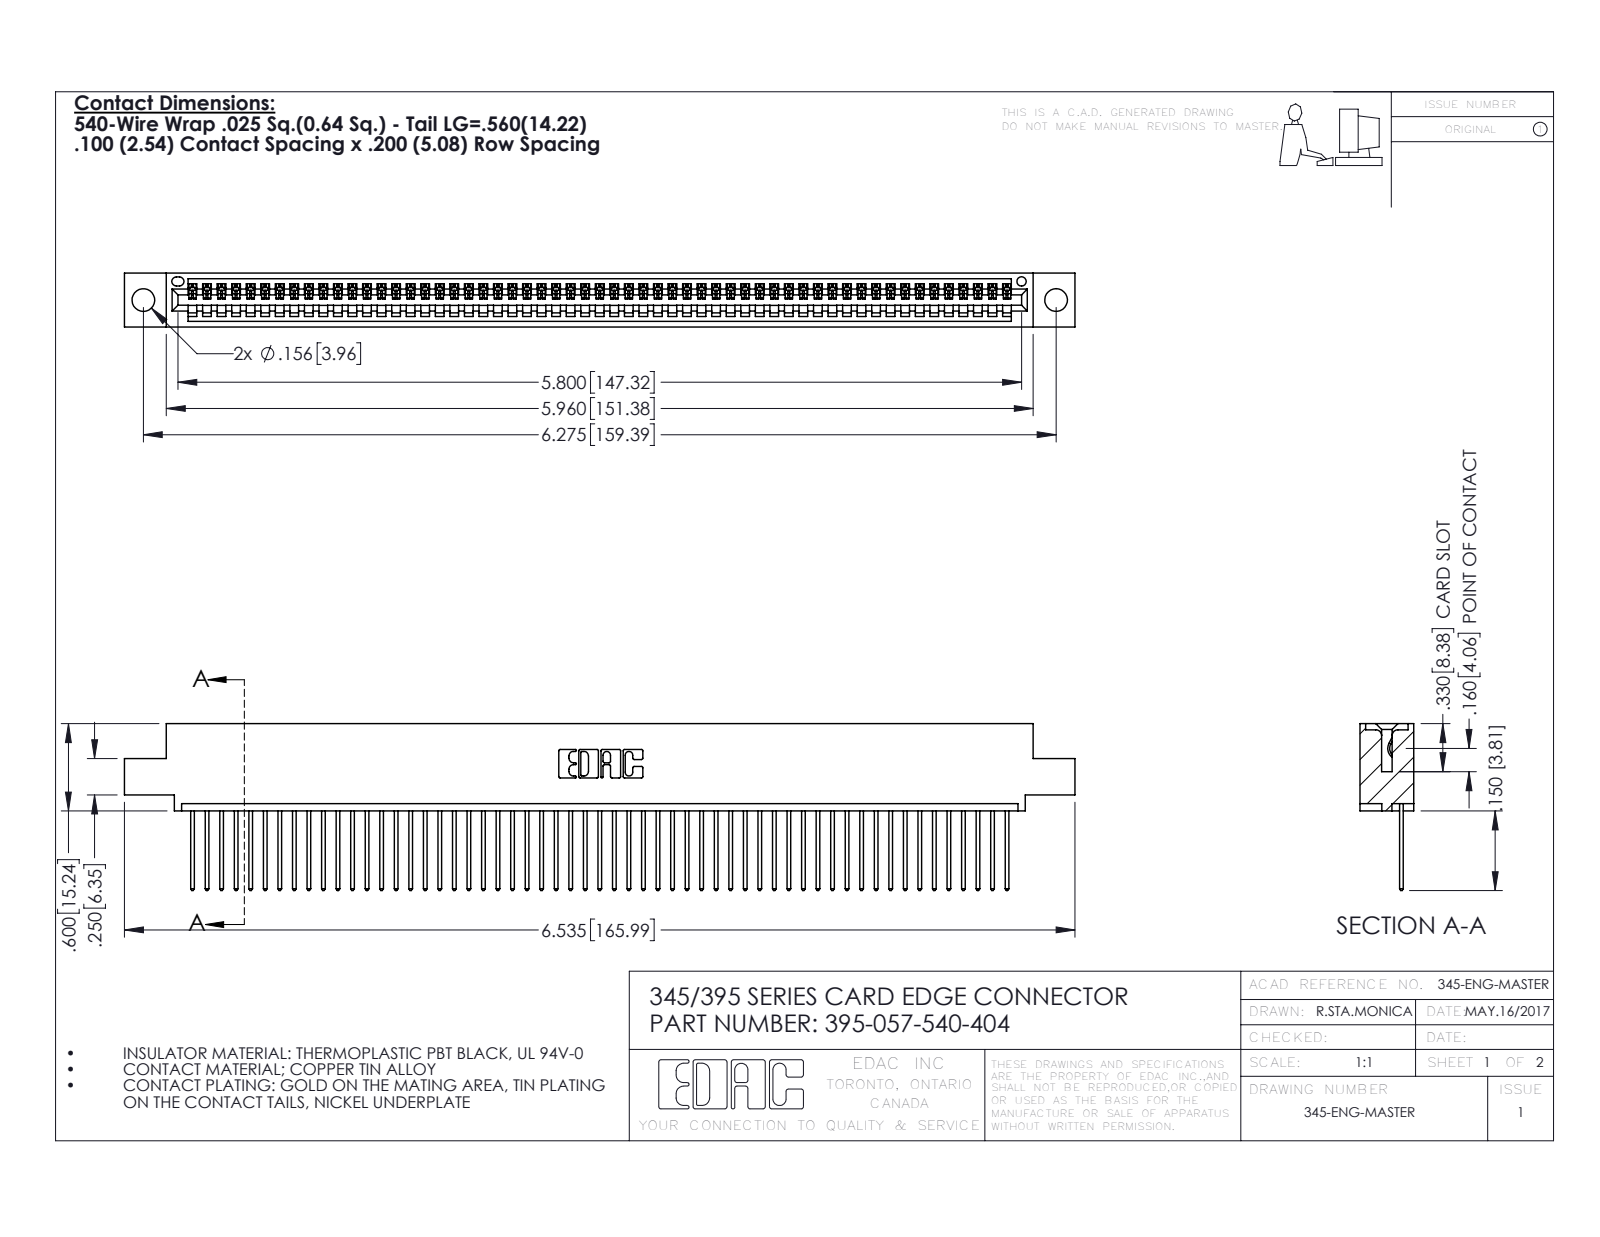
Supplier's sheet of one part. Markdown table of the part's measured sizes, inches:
| quantity | value |
| --- | --- |
| part name | 345 Part_0.110 Offset - 0.156 Dia-TH; 395-057-540-404; 345-292-001_345-293-140 |
| STEP written by | SolidWorks 2016 (CONFIG_CONTROL_DESIGN) |
| units | inches |
| bodies | 58 solids, 3436 faces (2364 planar, 1072 cylindrical, 0 other) |
| overall size | 6.535 × 1.147 × 0.37 |
| volume | 0.964 in³ |
| surface area | 33.56 in² |
| round holes (diameter × count) | 0.156 × 2, 0.064 × 1 |
| partial cylindrical surfaces (radius × count) | 0.006 × 114, 0.01 × 114, 0.01 × 22, 0.007 × 6, 0.031 × 6, 0.026 × 3, 0.031 × 2, 0.04 × 2 |
| main face-to-face distances | 0.298, 0.072, 0.37, 0.098, 0.272, 0.025, 0.2, 0.225, 0.149, 0.072 |
| hole center spacings | 0.27, 6.039, 6.275 |
